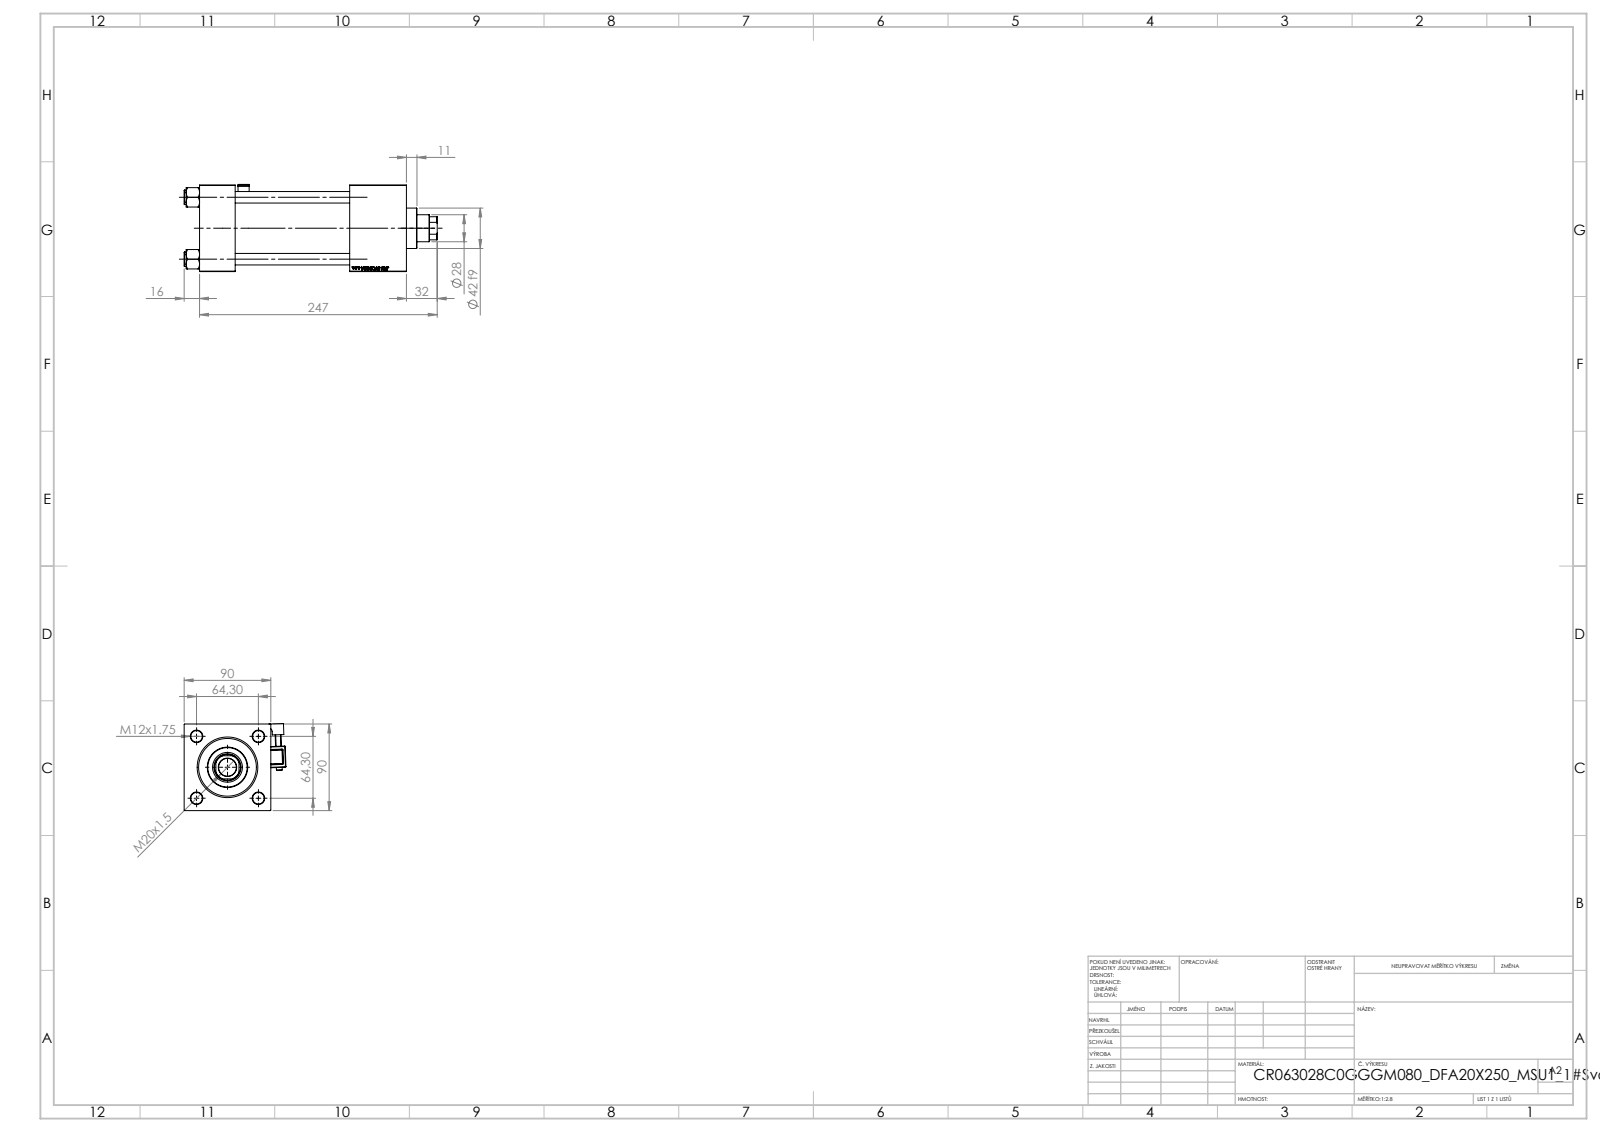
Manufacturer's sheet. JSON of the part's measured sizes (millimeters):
{"part_name": "V215CR_C_Body; FEMALE_PART_FOR_DFA; V215_VC_A; V215CR_MSU (+3 more)", "step_written_by": "SolidWorks 2019 (CONFIG_CONTROL_DESIGN)", "units": "millimeters", "bodies": {"solids": 13, "faces": 1259, "planar": 567, "cylindrical": 126, "other": 566}, "overall_size": [263, 105.78, 90.53], "volume_mm3": 1093000, "surface_area_mm2": 232128, "round_holes": [[12, 4], [7, 2], [20.96, 2], [30, 2], [18.5, 1], [28, 1], [31, 1], [50, 1], [60, 1], [63, 1]], "round_bosses_or_shafts": [[15, 4], [69, 1], [42, 1], [36, 1], [30, 1], [20, 1], [18, 1], [6, 1]], "partial_cylinders_radius": [[0.5, 24], [1, 1], [2.5, 1], [4, 1], [7.5, 1], [12, 1], [13.5, 1]], "face_to_face_distances": [90, 37, 215, 178, 156, 119, 59, 186.3, 149.3, 30.3], "hole_center_spacings": [45.47, 64.3, 90.93, 157.5]}
